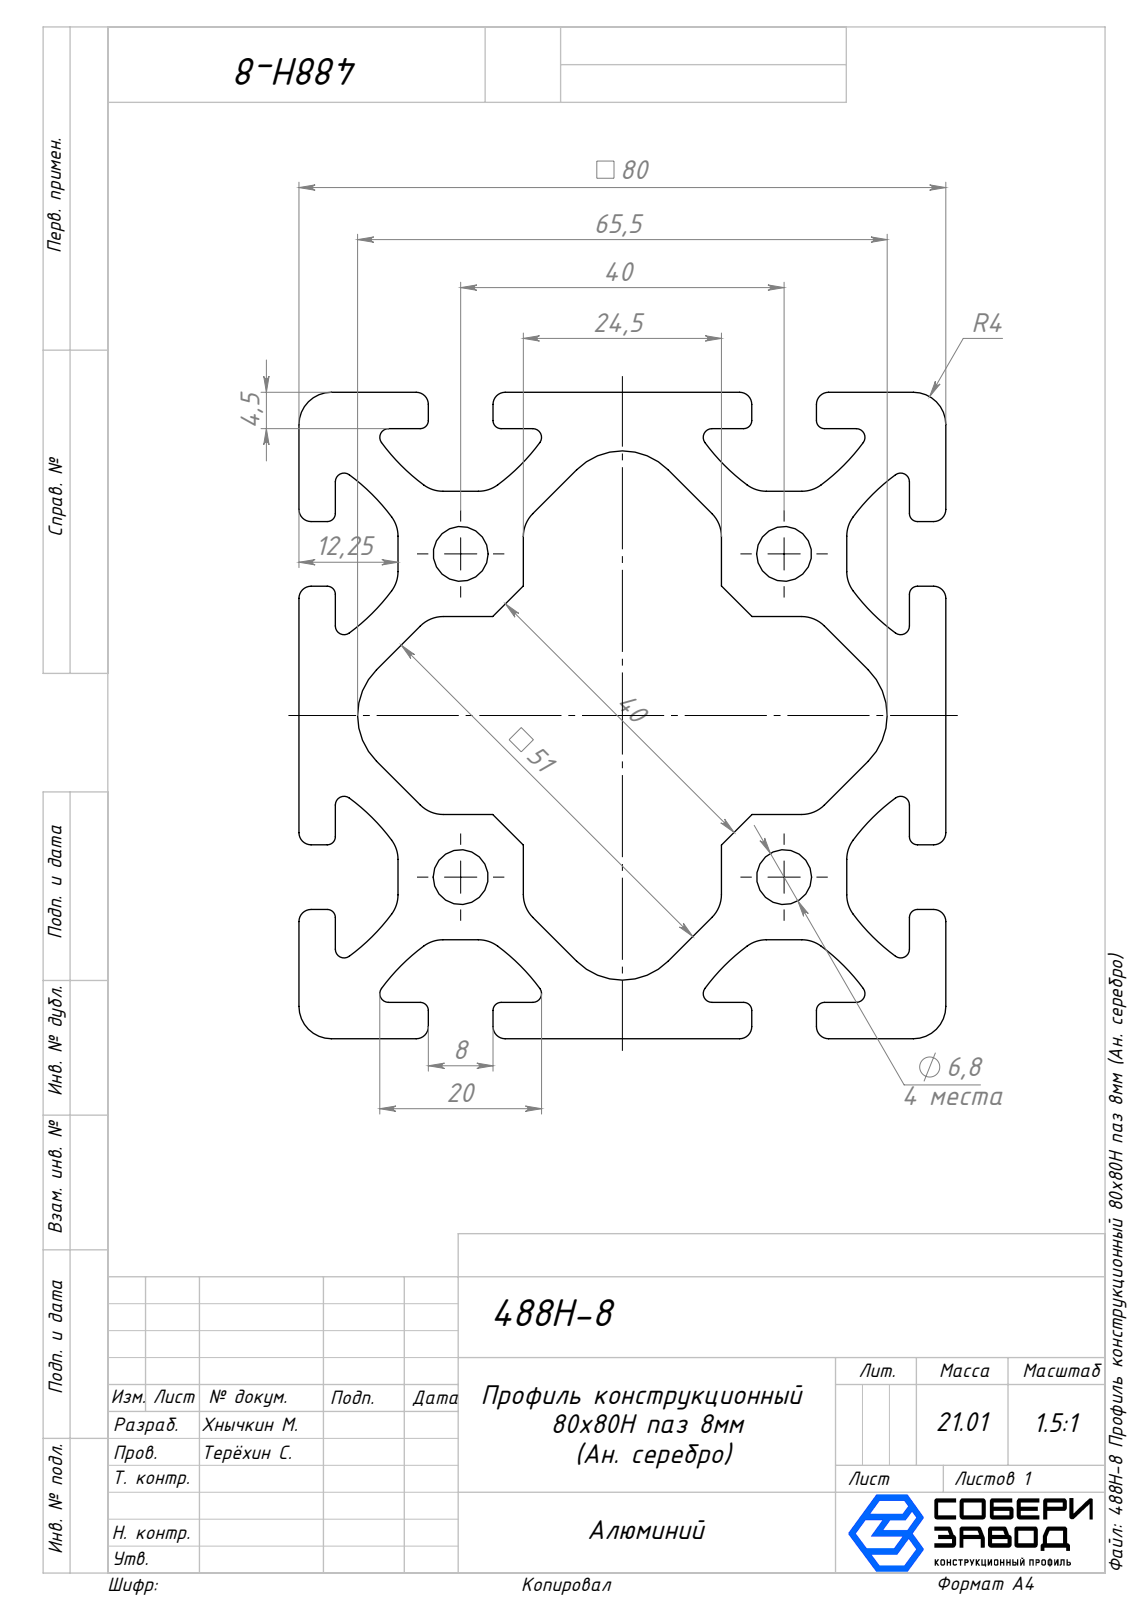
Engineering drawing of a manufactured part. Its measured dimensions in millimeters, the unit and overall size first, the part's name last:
Units: millimetres
Overall size (bounding box): 1000 × 80 × 80
Round holes (diameter × count): ⌀6.8 ×4
Partial cylindrical surfaces — rounded edges, fillets, slot ends (radius × count): R4 ×28, R1 ×16, R1.08 ×16, R1.5 ×16, R25 ×16, R8 ×4
Main face-to-face distances: 80, 4.5, 75.5, 40, 52.25, 47.75, 27.75, 23.25, 12.25, 67.75
Hole centre spacings: 40, 56.57
Volume: 2 694 000 mm³ · Surface area: 913 518 mm²
Bodies: 1 solid, 183 faces (74 planar, 109 cylindrical, 0 other)
Part name (STEP PRODUCT): V053-8953
STEP written by: SolidWorks 2025 (AUTOMOTIVE_DESIGN)
